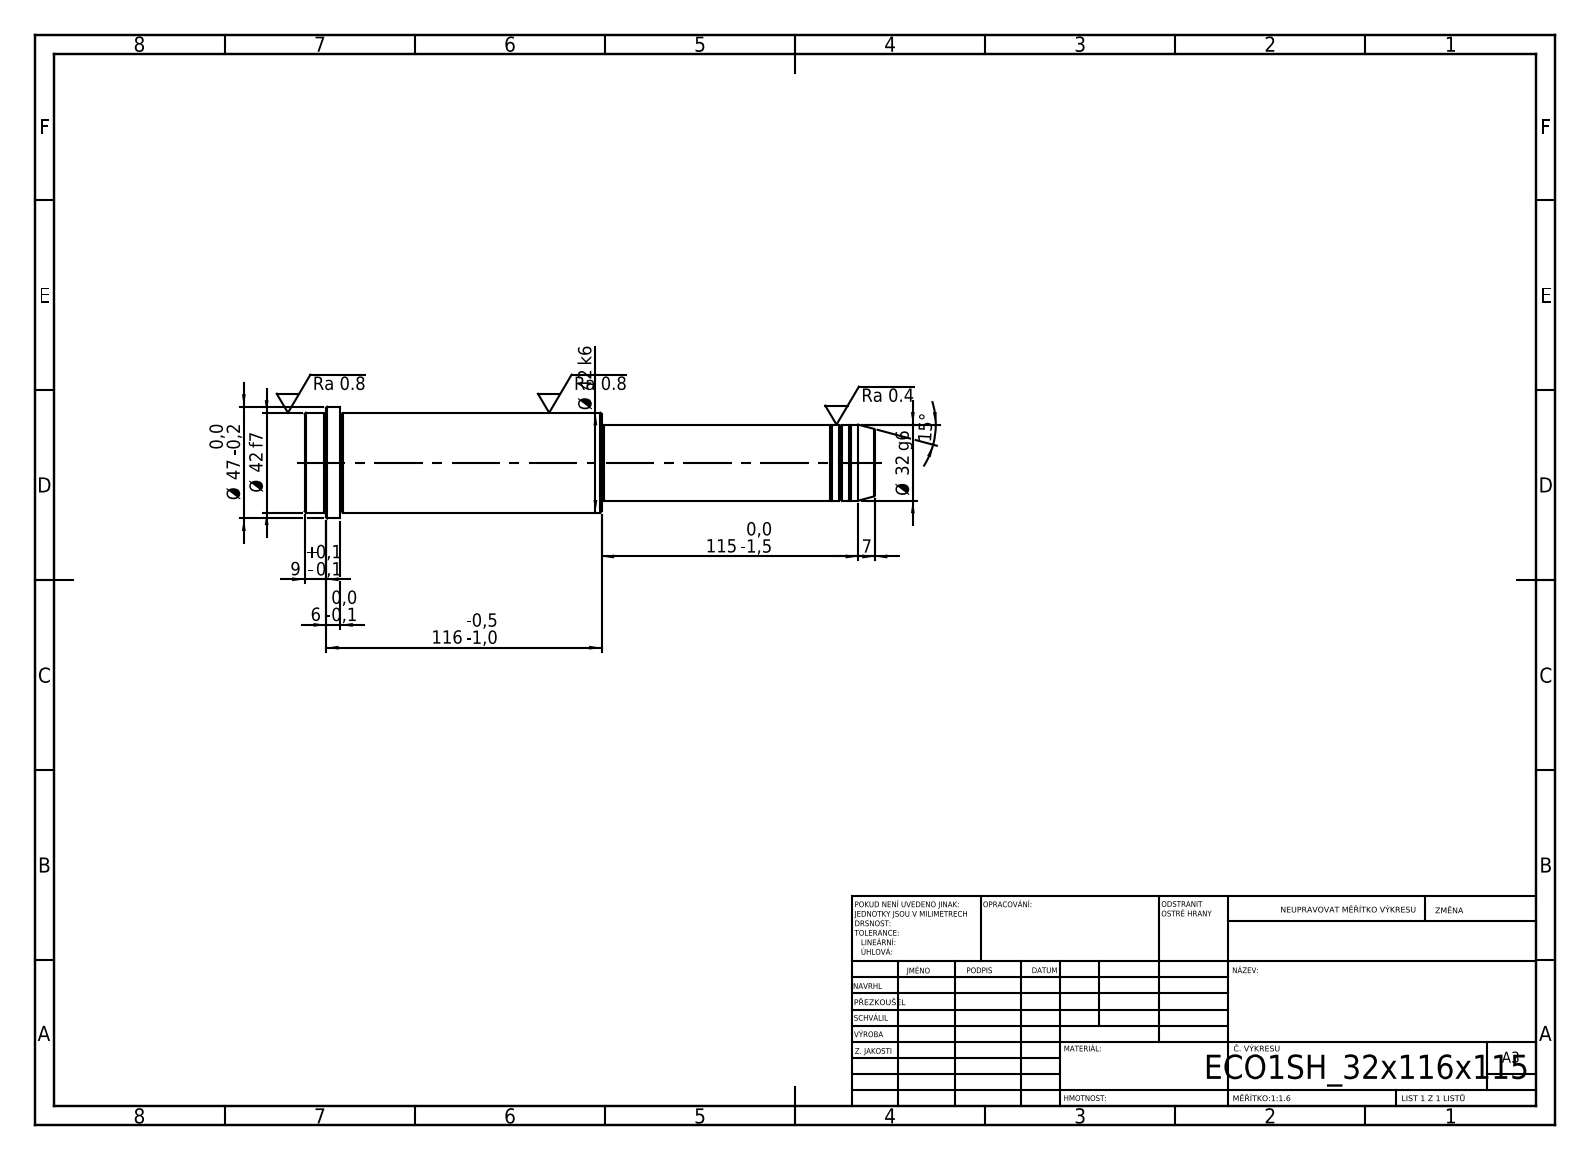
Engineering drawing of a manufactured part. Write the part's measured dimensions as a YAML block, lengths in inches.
step_written_by: "SolidWorks 2019 (CONFIG_CONTROL_DESIGN)"
units: inches
bodies: {solids: 1, faces: 52, planar: 6, cylindrical: 16, other: 30}
overall_size: [9.449, 1.85, 1.85]
volume: 16.28
surface_area: 49.13
round_bosses_or_shafts:
  - {diameter: 1.85, count: 1}
  - {diameter: 1.654, count: 1}
  - {diameter: 1.26, count: 1}
  - {diameter: 1.22, count: 1}
face_to_face_distances: [9.449, 4.528, 4.921, 8.858, 4.331, 0.591, 9.094, 4.567, 0.236, 0.354]
